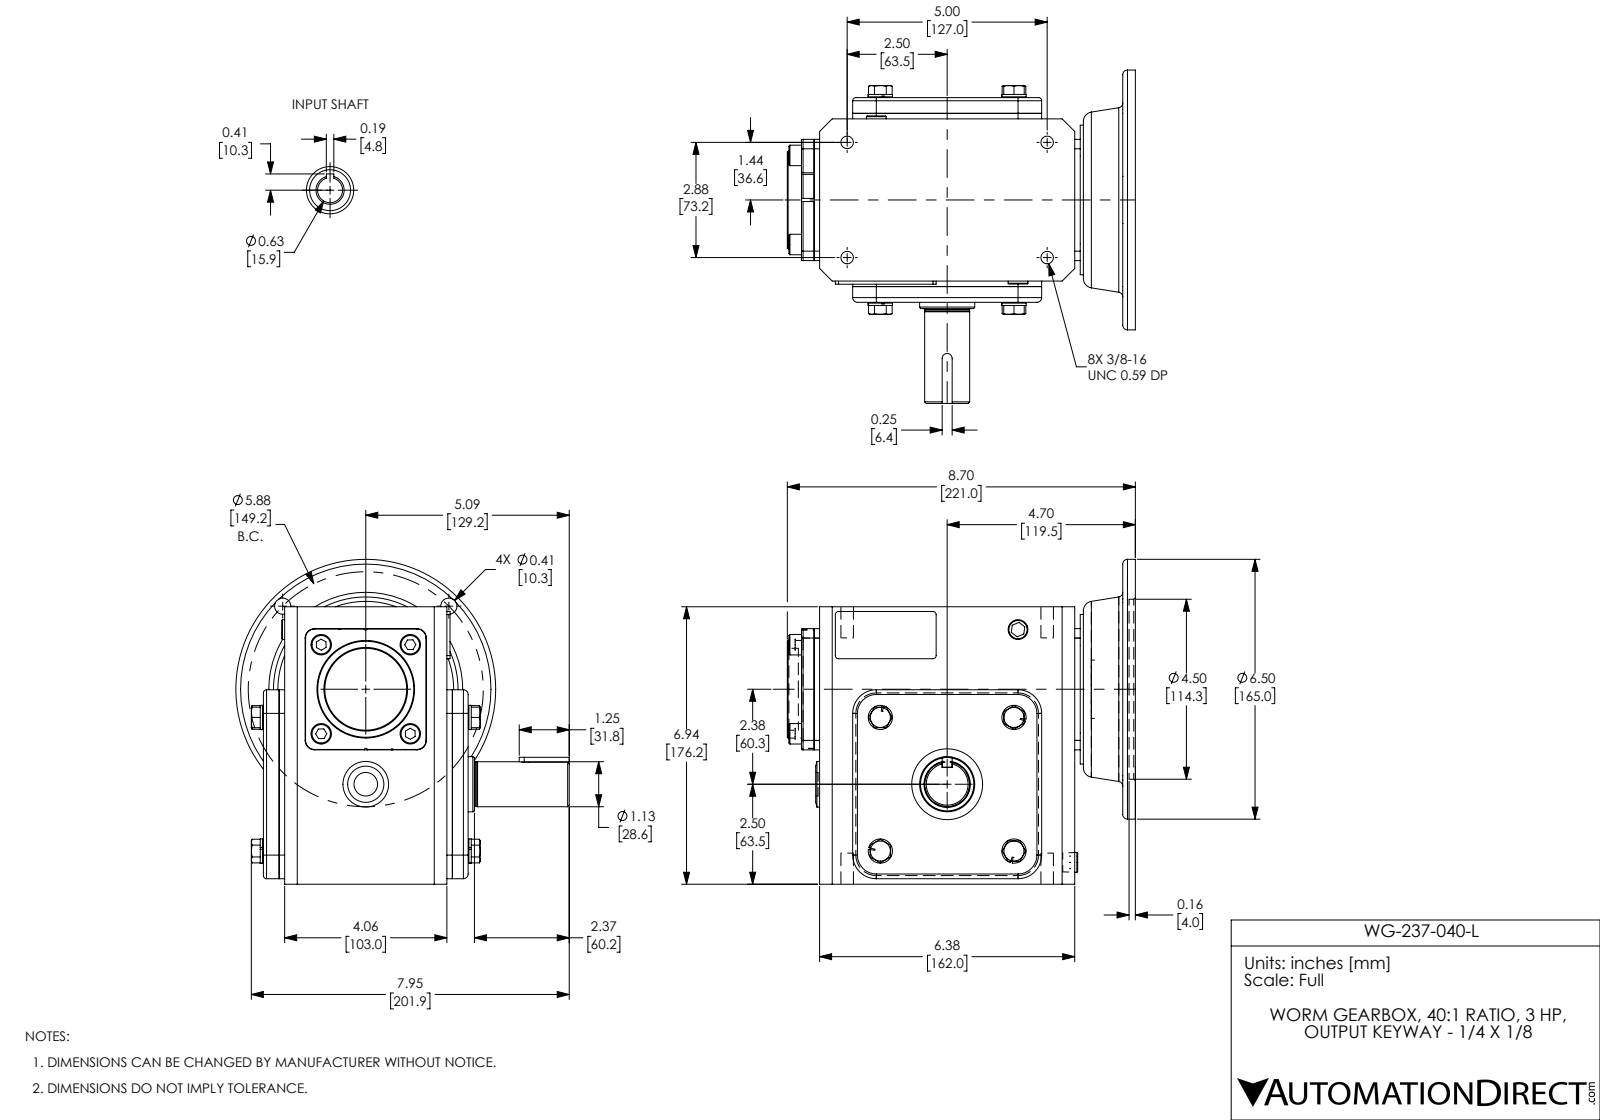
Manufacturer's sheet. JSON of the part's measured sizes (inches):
{"part_name": "WG-237-040-L", "step_written_by": "SolidWorks 2017 (AUTOMOTIVE_DESIGN)", "units": "inches", "bodies": {"solids": 37, "faces": 542, "planar": 295, "cylindrical": 157, "other": 90}, "overall_size": [8.701, 8.335, 8.123], "volume_in3": 220.2, "surface_area_in2": 513.5, "round_holes": [[0.313, 4], [0.406, 4], [0.591, 1], [0.625, 1], [1.181, 1], [1.378, 1], [1.457, 1], [1.772, 1], [3.819, 1], [4.5, 1]], "round_bosses_or_shafts": [[0.606, 4], [0.512, 4], [6.496, 1], [3.74, 1], [2.441, 1], [2.047, 1], [1.142, 1], [1.125, 1]], "partial_cylinders_radius": [[0.079, 12], [0.236, 6], [0.118, 4], [0.591, 4], [0.02, 2], [0.039, 2], [0.125, 1]], "face_to_face_distances": [0.138, 4.724, 0.394, 4.331, 0.531, 4.193, 4.587, 6.516, 6.937, 0.315], "hole_center_spacings": [2.937, 2.098, 2.88, 4.154, 4.154, 4.913, 5, 5.77]}
